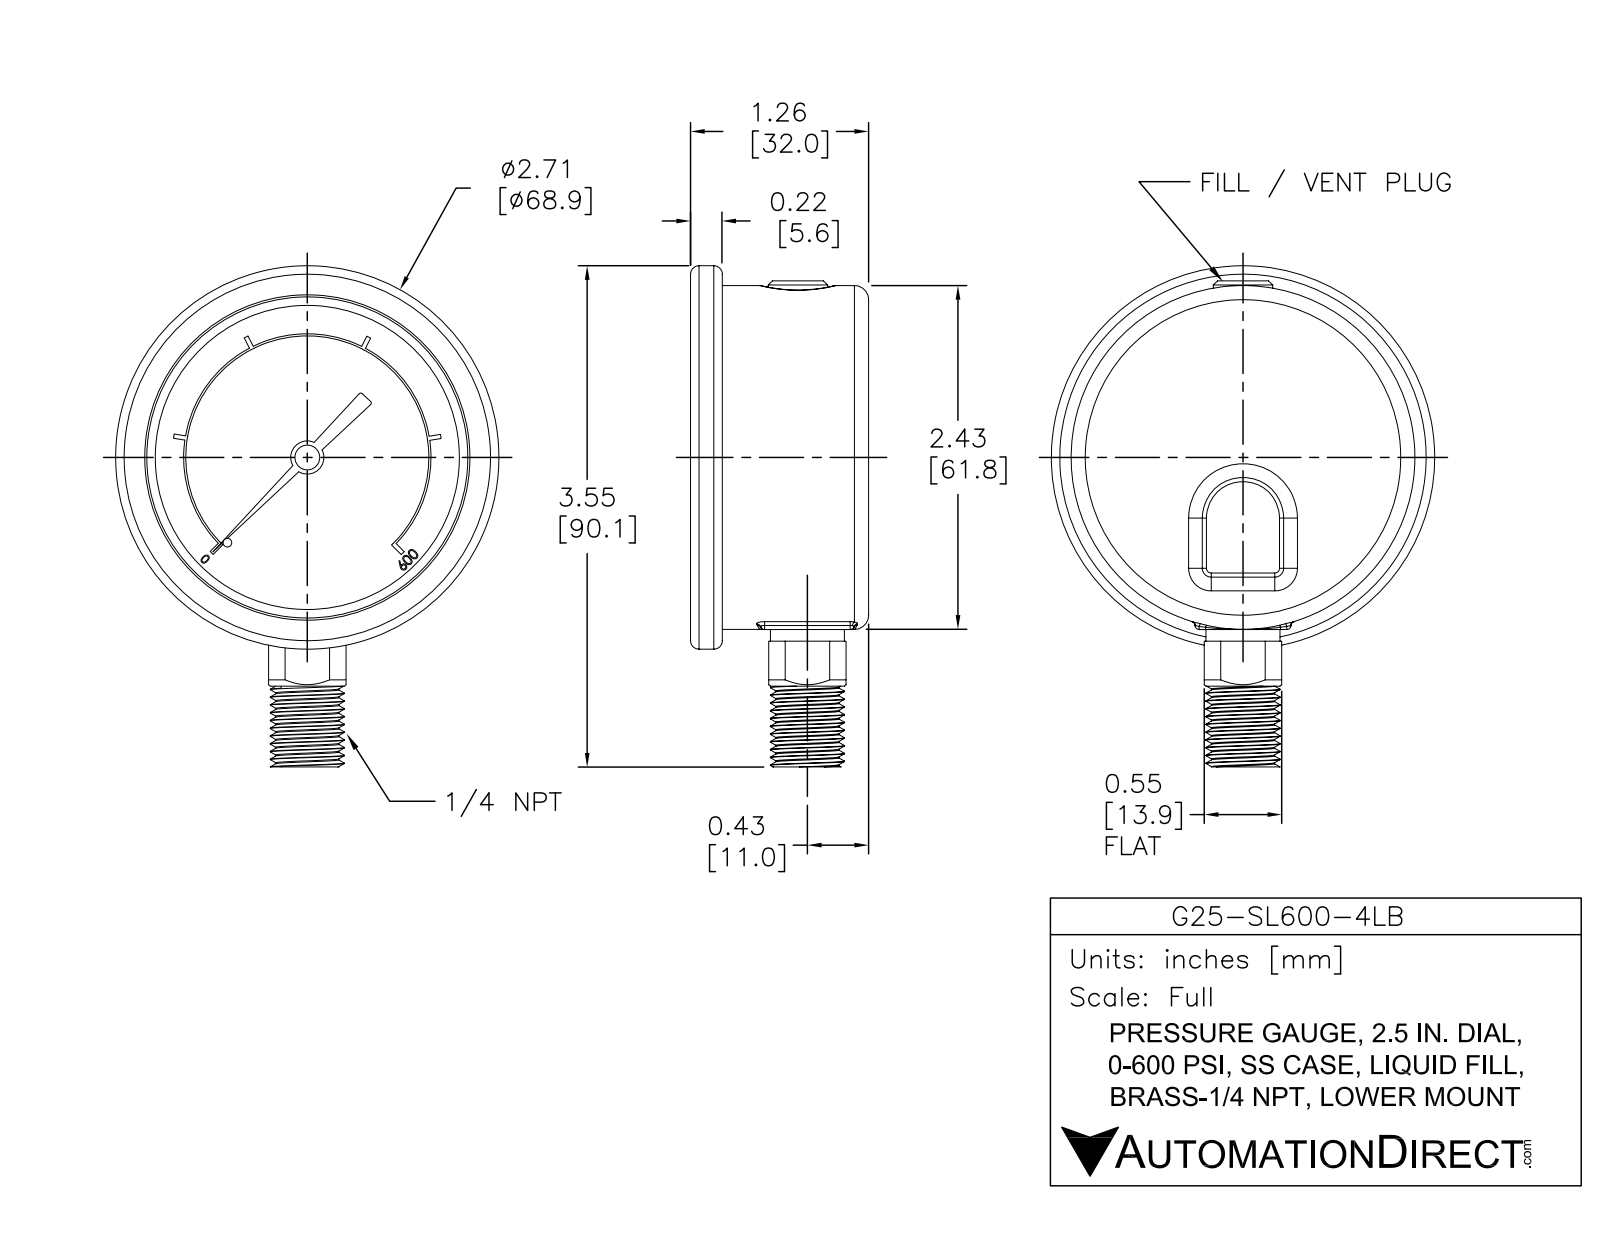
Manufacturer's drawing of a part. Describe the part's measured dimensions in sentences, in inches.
The part is named "G25-SL600-4LB". Its 3-D file was written by "SolidWorks 2021 (AUTOMOTIVE_DESIGN)". It is 1 solid with 350 faces: 193 planar, 85 cylindrical and 72 other. Overall it measures 3.546 by 2.713 by 1.26 inches. Its volume is 5.273 cubic inches and its surface area 24.68 square inches. Round holes: 1 of diameter 0.027, 1 of diameter 0.071, 1 of diameter 0.119, 1 of diameter 2.272. Round bosses or shafts: 1 of diameter 2.713, 1 of diameter 2.433, 1 of diameter 0.524, 1 of diameter 0.42, 1 of diameter 0.235, 1 of diameter 0.176, 1 of diameter 0.14, 1 of diameter 0.041. Partial cylindrical surfaces (rounded edges, fillets, slot ends): 9 of radius 0.03, 3 of radius 0.1, 2 of radius 0.015, 1 of radius 0.316, 1 of radius 0.86, 1 of radius 0.875. The main face-to-face distances are 1.01, 1.26, 0.25, 1.035, 0.025, 0.225, 0.1, 0.91, 0.935, 1.16. The hole center spacings are 0.067.
